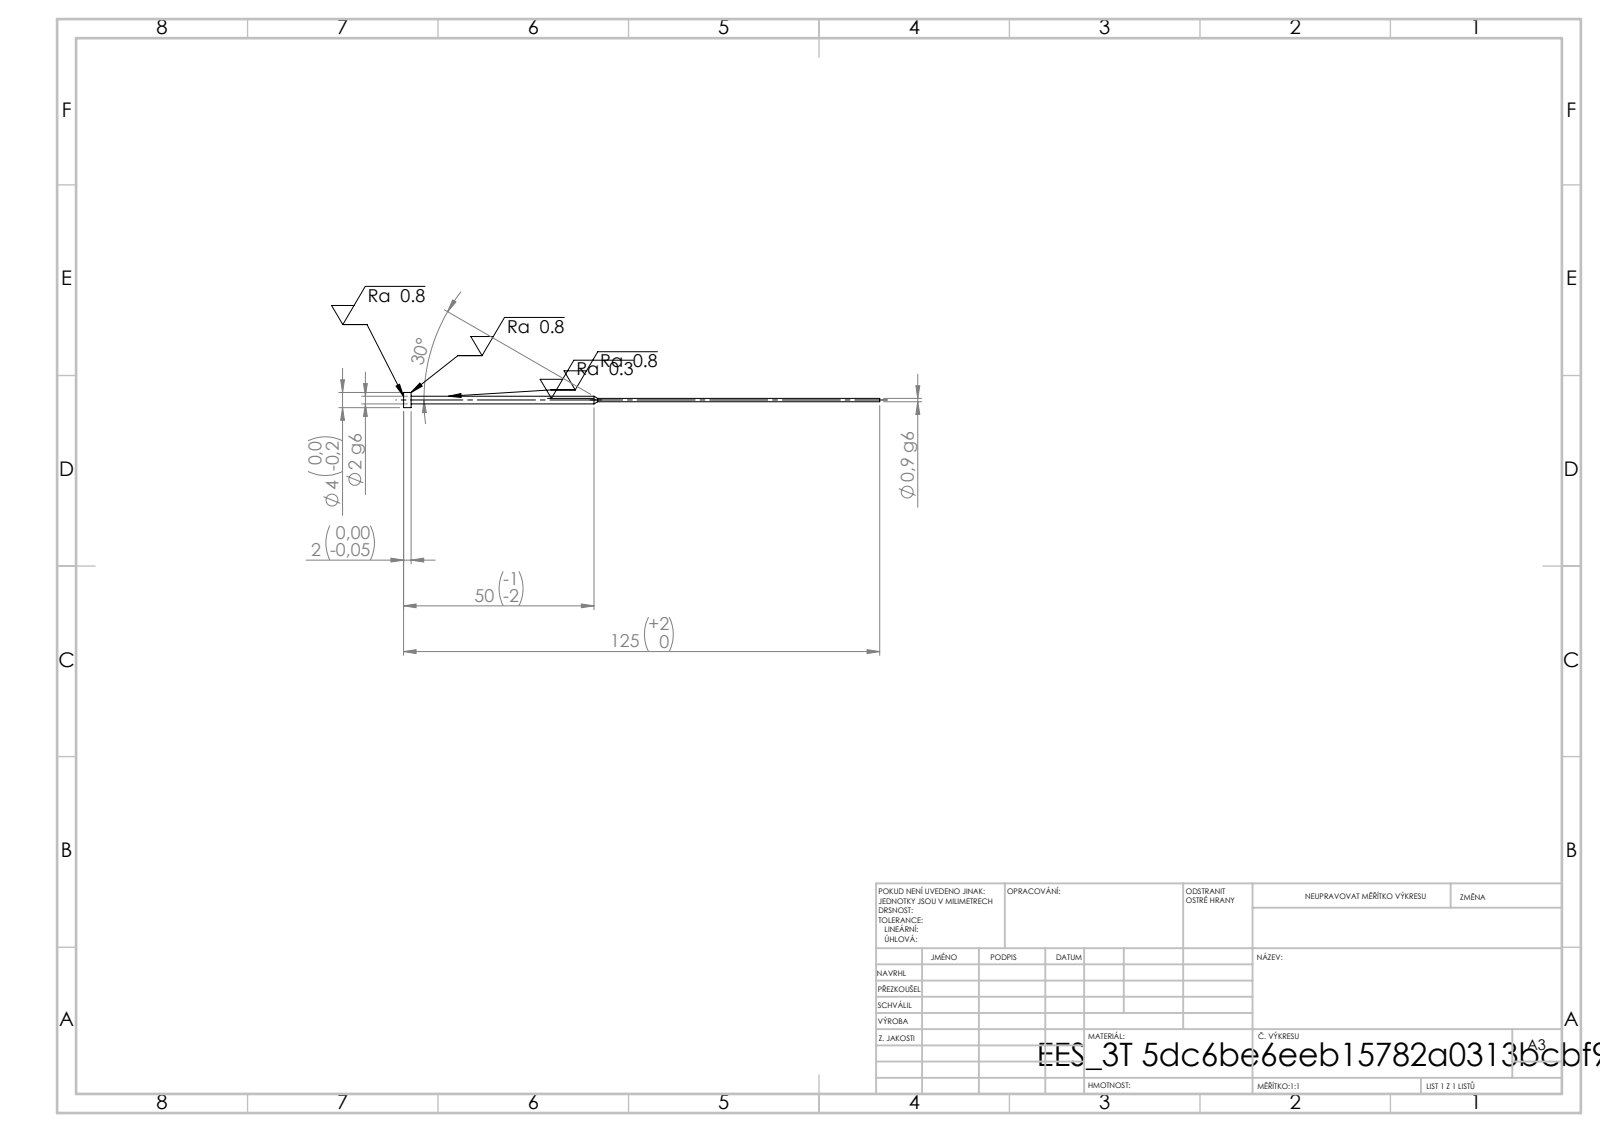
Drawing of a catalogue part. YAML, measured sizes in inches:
step_written_by: "SolidWorks 2019 (CONFIG_CONTROL_DESIGN)"
units: inches
bodies: {solids: 1, faces: 11, planar: 3, cylindrical: 6, other: 2}
overall_size: [4.921, 0.157, 0.157]
volume: 0.014
surface_area: 0.874
round_bosses_or_shafts:
  - {diameter: 0.157, count: 1}
  - {diameter: 0.079, count: 1}
  - {diameter: 0.035, count: 1}
face_to_face_distances: [0.079, 4.843, 4.921]
